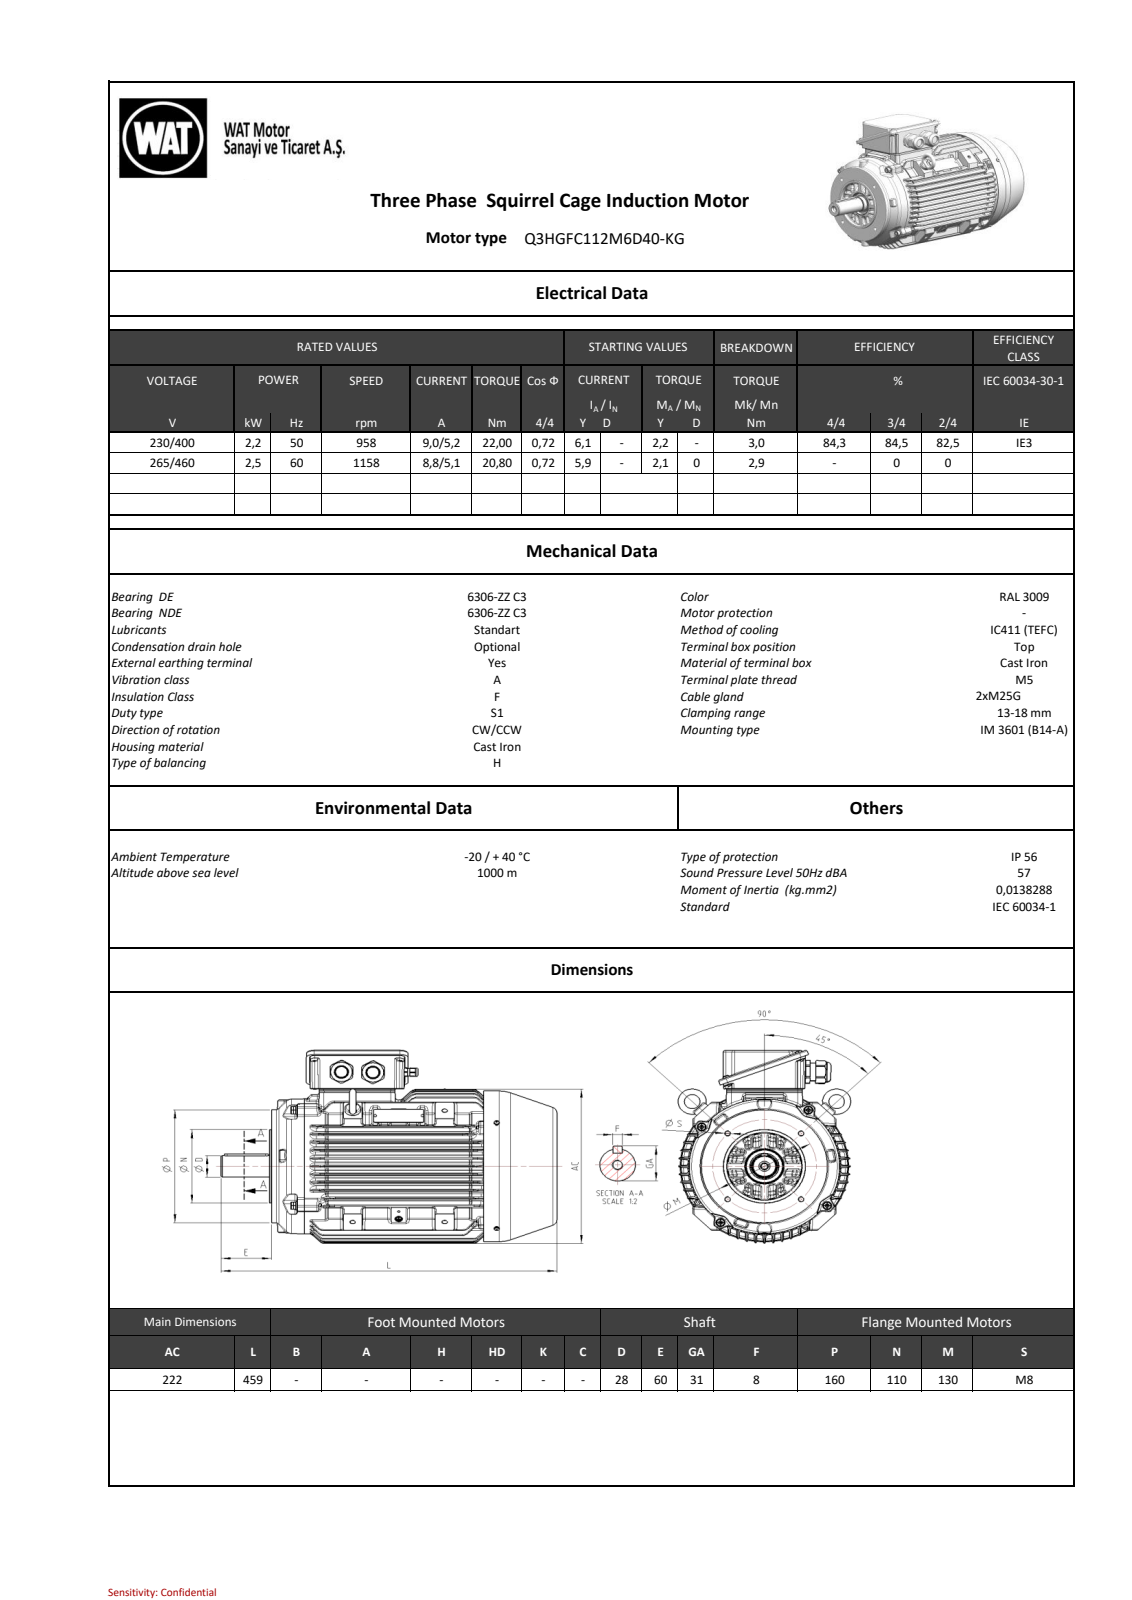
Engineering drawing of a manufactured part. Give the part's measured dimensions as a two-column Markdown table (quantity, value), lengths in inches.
| quantity | value |
| --- | --- |
| part name | 260037F440EAov9l |
| STEP written by | SIEMENS PLM Software NX 11.0 (AUTOMOTIVE_DESIGN) |
| units | inches |
| bodies | 0 solids, 4738 faces (896 planar, 1360 cylindrical, 2482 other) |
| overall size | 18.248 × 11.363 × 8.72 |
| round holes (diameter × count) | 0.197 × 10, 0.177 × 6, 0.268 × 6, 0.138 × 5, 0.335 × 5, 0.394 × 4, 0.098 × 2, 0.13 × 2, 0.677 × 2, 0.157 × 1, 0.315 × 1, 0.413 × 1 |
| round bosses / shafts (diameter × count) | 0.394 × 4, 1.091 × 2, 0.994 × 2, 0.787 × 2, 0.472 × 2, 8.465 × 1, 7.559 × 1, 4.331 × 1 |
| partial cylindrical surfaces (radius × count) | 0.157 × 267, 0.02 × 142, 0.118 × 100, 0.059 × 96, 0.079 × 57, 0.071 × 41, 0.039 × 29, 0.01 × 21 |
| main face-to-face distances | 0.516, 1.035, 0.519, 1.557, 1.041, 0.522, 3.565, 1.573, 2.081, 1.565 |
| hole center spacings | 2.571, 1.373, 3.819, 4.212, 4.528, 4.952, 5.401, 6.355 |
